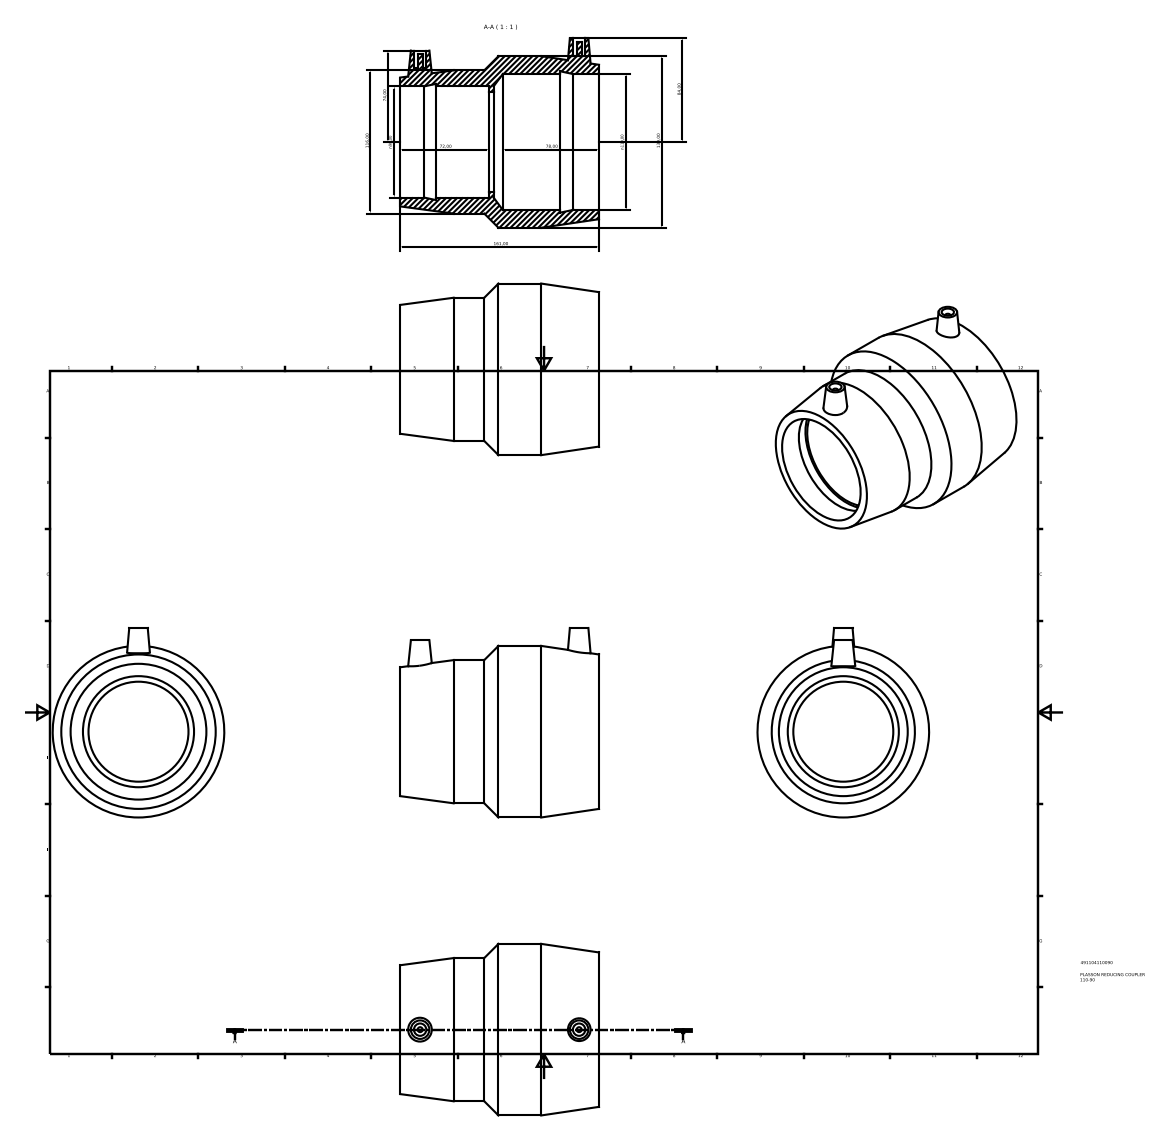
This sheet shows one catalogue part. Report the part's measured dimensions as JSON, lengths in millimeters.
{"part_name": "491104110090", "step_written_by": "Autodesk Inventor 2015 (AUTOMOTIVE_DESIGN)", "units": "millimeters", "bodies": {"solids": 1, "faces": 31, "planar": 12, "cylindrical": 11, "other": 8}, "overall_size": [161, 153.5, 139], "volume_mm3": 713467, "surface_area_mm2": 129661, "round_holes": [[10, 2], [81, 1], [90, 1], [110, 1]], "round_bosses_or_shafts": [[4, 2], [139, 1], [116, 1]], "face_to_face_distances": [161, 75.6, 85.4, 72, 3.6, 89, 129.8, 57.8, 54.2, 31.2], "hole_center_spacings": [128.8]}
